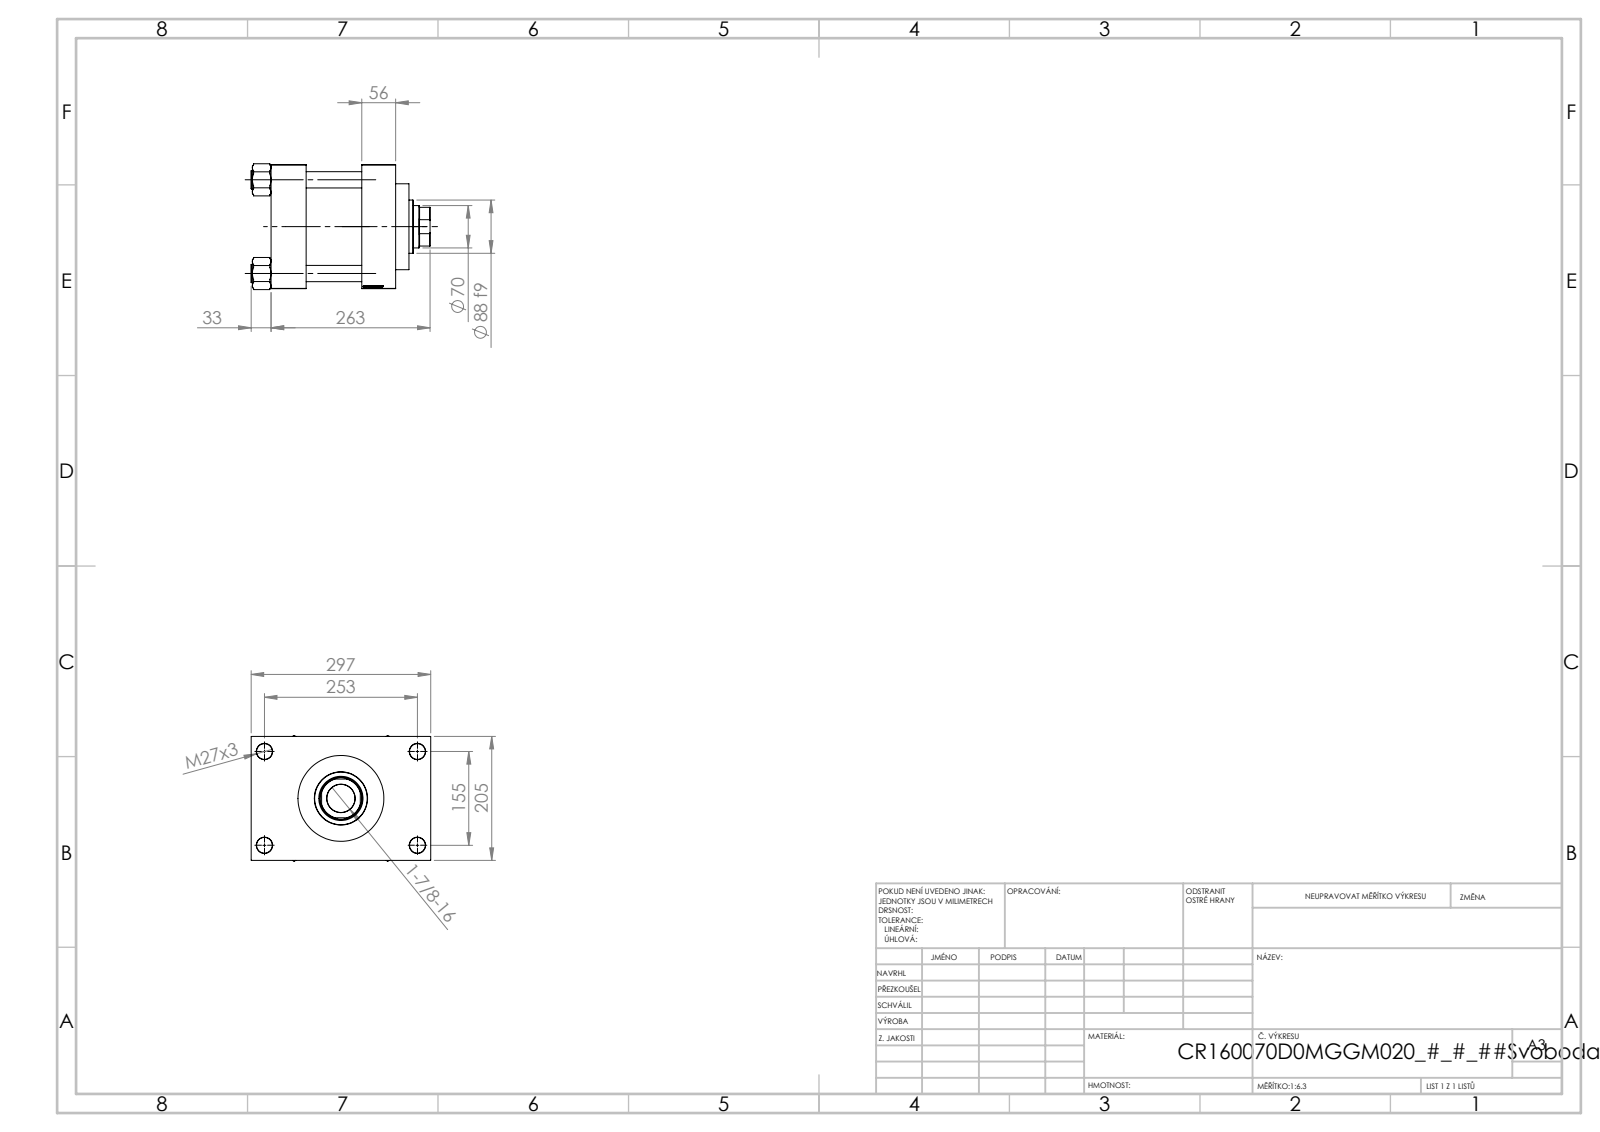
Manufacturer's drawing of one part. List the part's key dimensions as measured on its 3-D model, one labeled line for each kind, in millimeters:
Part name (STEP PRODUCT): NUT_M5_D; V215CR_D_Body; V215CR_VCP_D; V215CR_D_TYCINKA (+1 more)
STEP written by: SolidWorks 2019 (CONFIG_CONTROL_DESIGN)
Units: millimetres
Bodies: 11 solids, 1149 faces (544 planar, 87 cylindrical, 518 other)
Overall size (bounding box): 297 × 296 × 208.14
Volume: 7 896 000 mm³ · Surface area: 724 973 mm²
Round holes (diameter × count): ⌀26 ×4, ⌀27 ×4, ⌀7 ×2, ⌀33.24 ×2, ⌀45 ×2, ⌀46.5 ×1, ⌀70 ×1, ⌀73 ×1, ⌀120 ×1, ⌀142 ×1, ⌀160 ×1
Round bosses / shafts (diameter × count): ⌀30 ×4, ⌀166 ×1, ⌀88 ×1
Partial cylindrical surfaces — rounded edges, fillets, slot ends (radius × count): R34 ×1
Main face-to-face distances: 58, 150, 92, 206, 148, 56, 205, 46, 251, 72
Hole centre spacings: 49.05, 109.53, 148.35, 154.9, 162.53, 203.95, 256.13, 155
